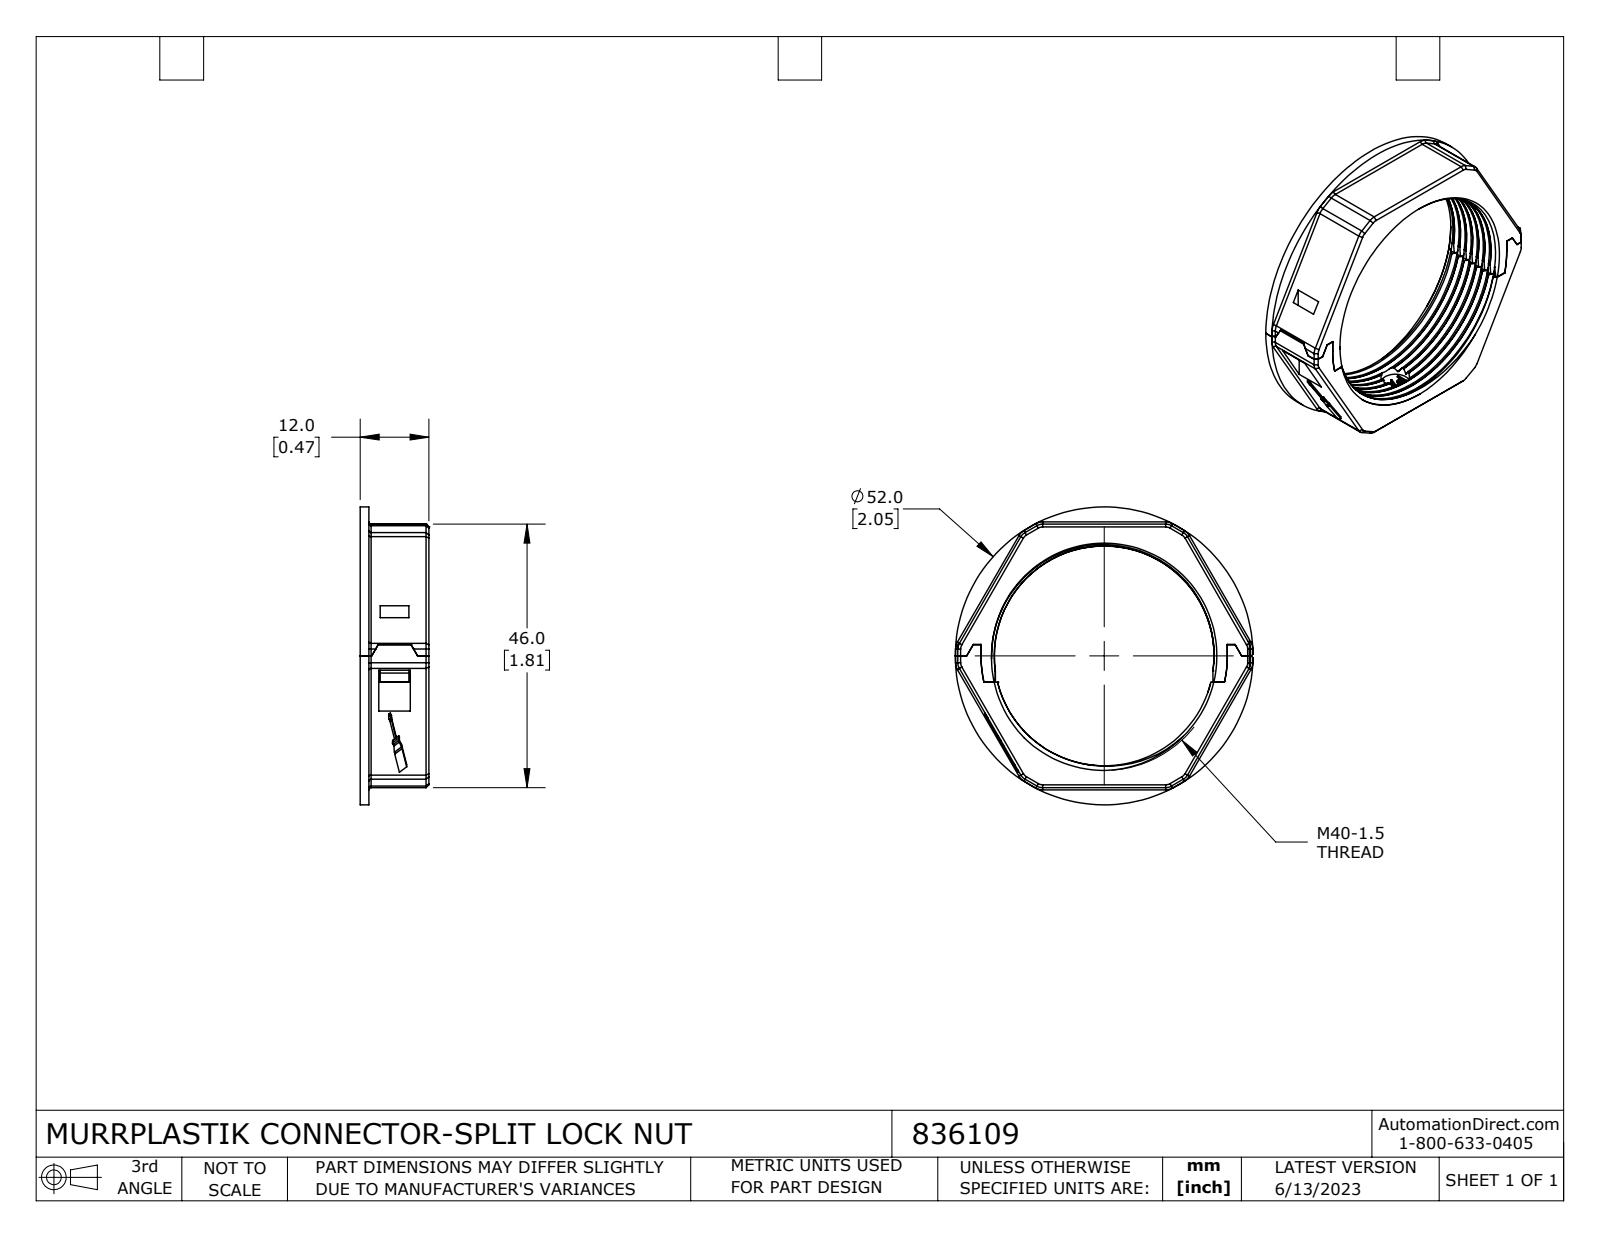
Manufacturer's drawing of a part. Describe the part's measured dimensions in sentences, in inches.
The part is named "836109". Its 3-D file was written by "SolidWorks 2021 (CONFIG_CONTROL_DESIGN)". It is 2 solids with 533 faces: 263 planar, 100 cylindrical and 170 other. Overall it measures 2.047 by 2.047 by 0.472 inches. Its volume is 0.465 cubic inches and its surface area 10.59 square inches. Round holes: 1 of diameter 0.197, 1 of diameter 0.315, 1 of diameter 1.51, 1 of diameter 1.575. Round bosses or shafts: 1 of diameter 2.047. Partial cylindrical surfaces (rounded edges, fillets, slot ends): 12 of radius 0.016, 12 of radius 0.079, 2 of radius 0.004, 2 of radius 0.02, 1 of radius 0.846. The main face-to-face distances are 0.472, 1.811, 0.059, 0.413, 1.693, 0.079, 0.256, 0.177, 0.807, 0.886.
